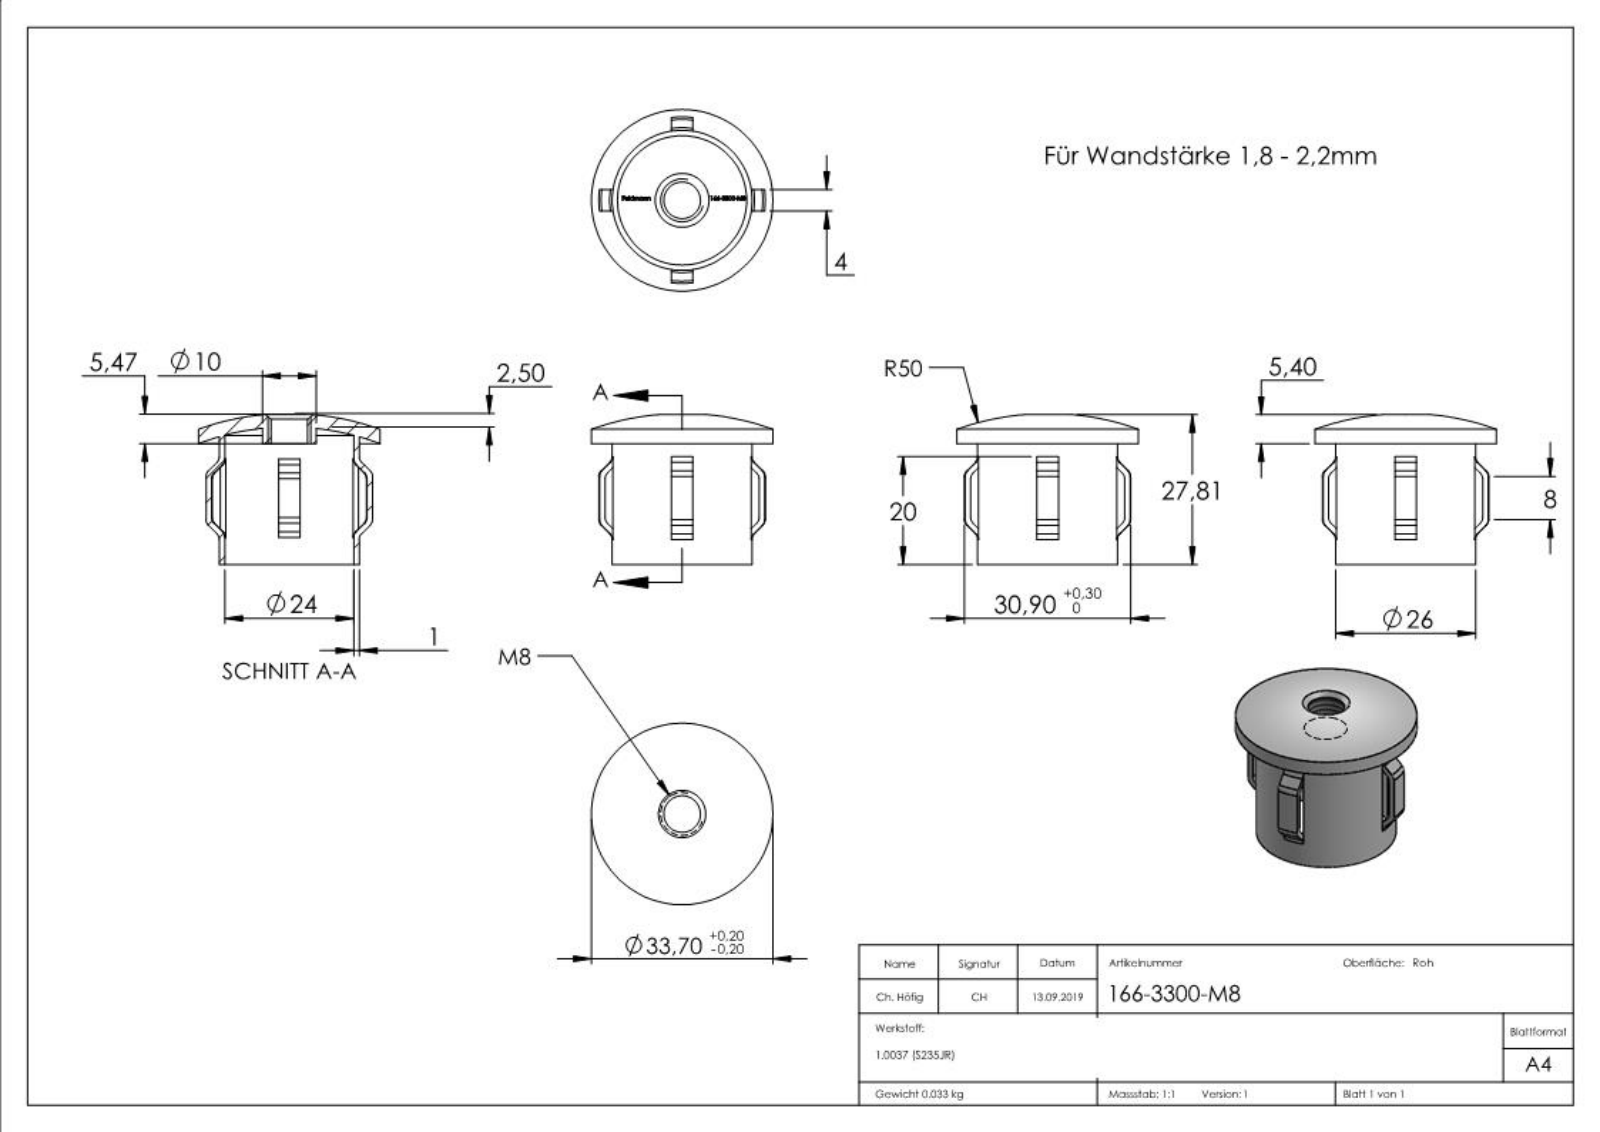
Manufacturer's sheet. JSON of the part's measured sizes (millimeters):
{"part_name": "166-3300-M8", "step_written_by": "SolidWorks 2015 (CONFIG_CONTROL_DESIGN)", "units": "millimeters", "bodies": {"solids": 1, "faces": 374, "planar": 111, "cylindrical": 20, "other": 243}, "overall_size": [33.7, 33.7, 27.81], "volume_mm3": 4225, "surface_area_mm2": 6262, "round_holes": [[6.8, 1], [24, 1]], "round_bosses_or_shafts": [[33.7, 1], [26, 1], [10, 1]], "partial_cylinders_radius": [[14.45, 1], [15.45, 1]], "face_to_face_distances": [4, 22.41, 1.78, 2, 1.21, 0.83, 0.99, 15.32, 0.44, 16.53]}
